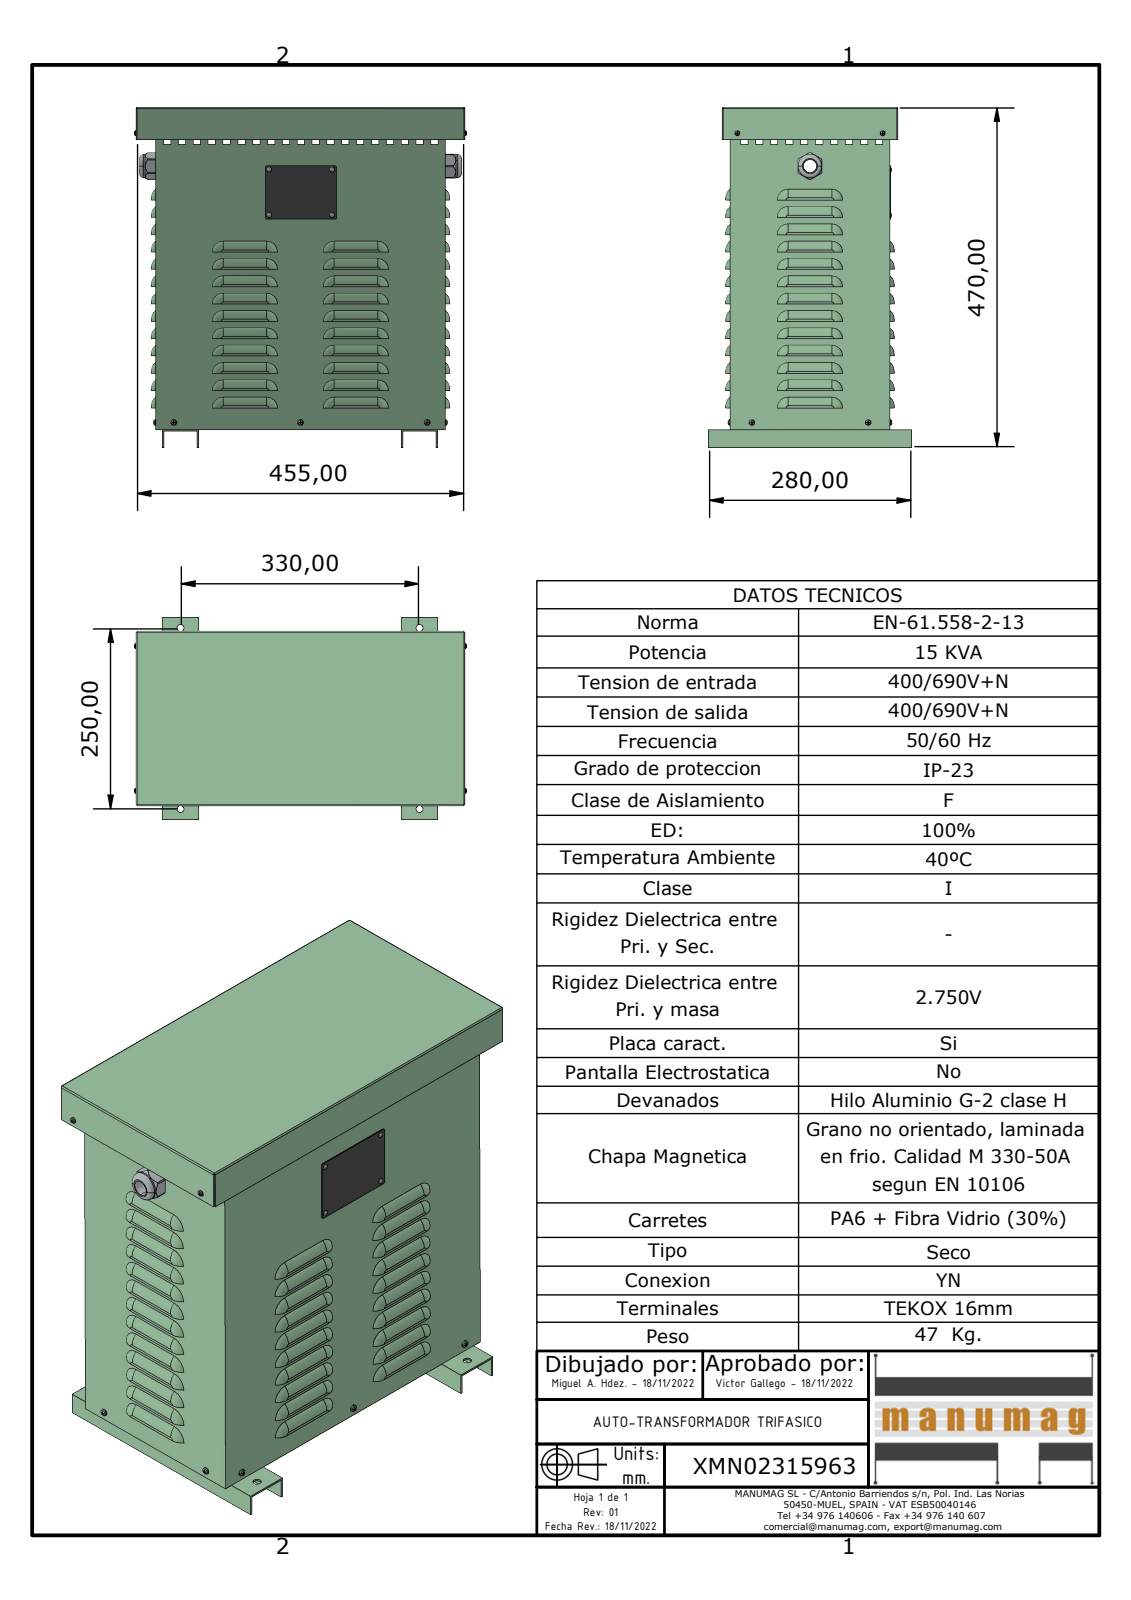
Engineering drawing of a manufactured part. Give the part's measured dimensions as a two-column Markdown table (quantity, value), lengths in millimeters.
| quantity | value |
| --- | --- |
| part name | XMN02315963; JE015 - JE020 - JE025 NACIONAL CUERPO; JE015 - JE020 - JE025 NACIONAL BASE; JE015 - JE020 - JE025 NACIONAL PATA (+6 more) |
| STEP written by | Autodesk Inventor 2023 (AUTOMOTIVE_DESIGN) |
| units | millimeters |
| bodies | 26 solids, 2110 faces (1086 planar, 450 cylindrical, 574 other) |
| overall size | 472.34 × 459.14 × 280.08 |
| volume | 1 655 000 mm³ |
| surface area | 1 781 000 mm² |
| round holes (diameter × count) | 4.5 × 12, 4 × 6, 9.6 × 4, 18 × 1, 30 × 1 |
| round bosses / shafts (diameter × count) | 4 × 8, 3.62 × 8, 3.2 × 4, 3.5 × 2, 3.18 × 2, 32.4 × 1, 28.5 × 1, 28.3 × 1 |
| partial cylindrical surfaces (radius × count) | 14 × 118, 4 × 49, 15 × 49, 3 × 16, 4.5 × 16, 1.5 × 8, 2 × 4, 18.6 × 1 |
| main face-to-face distances | 1.5, 218.5, 217, 445, 398.5, 220, 397, 446.5, 400, 443.5 |
| hole center spacings | 175, 63, 350, 0.5, 87, 87.5, 107.42, 107.82 |
